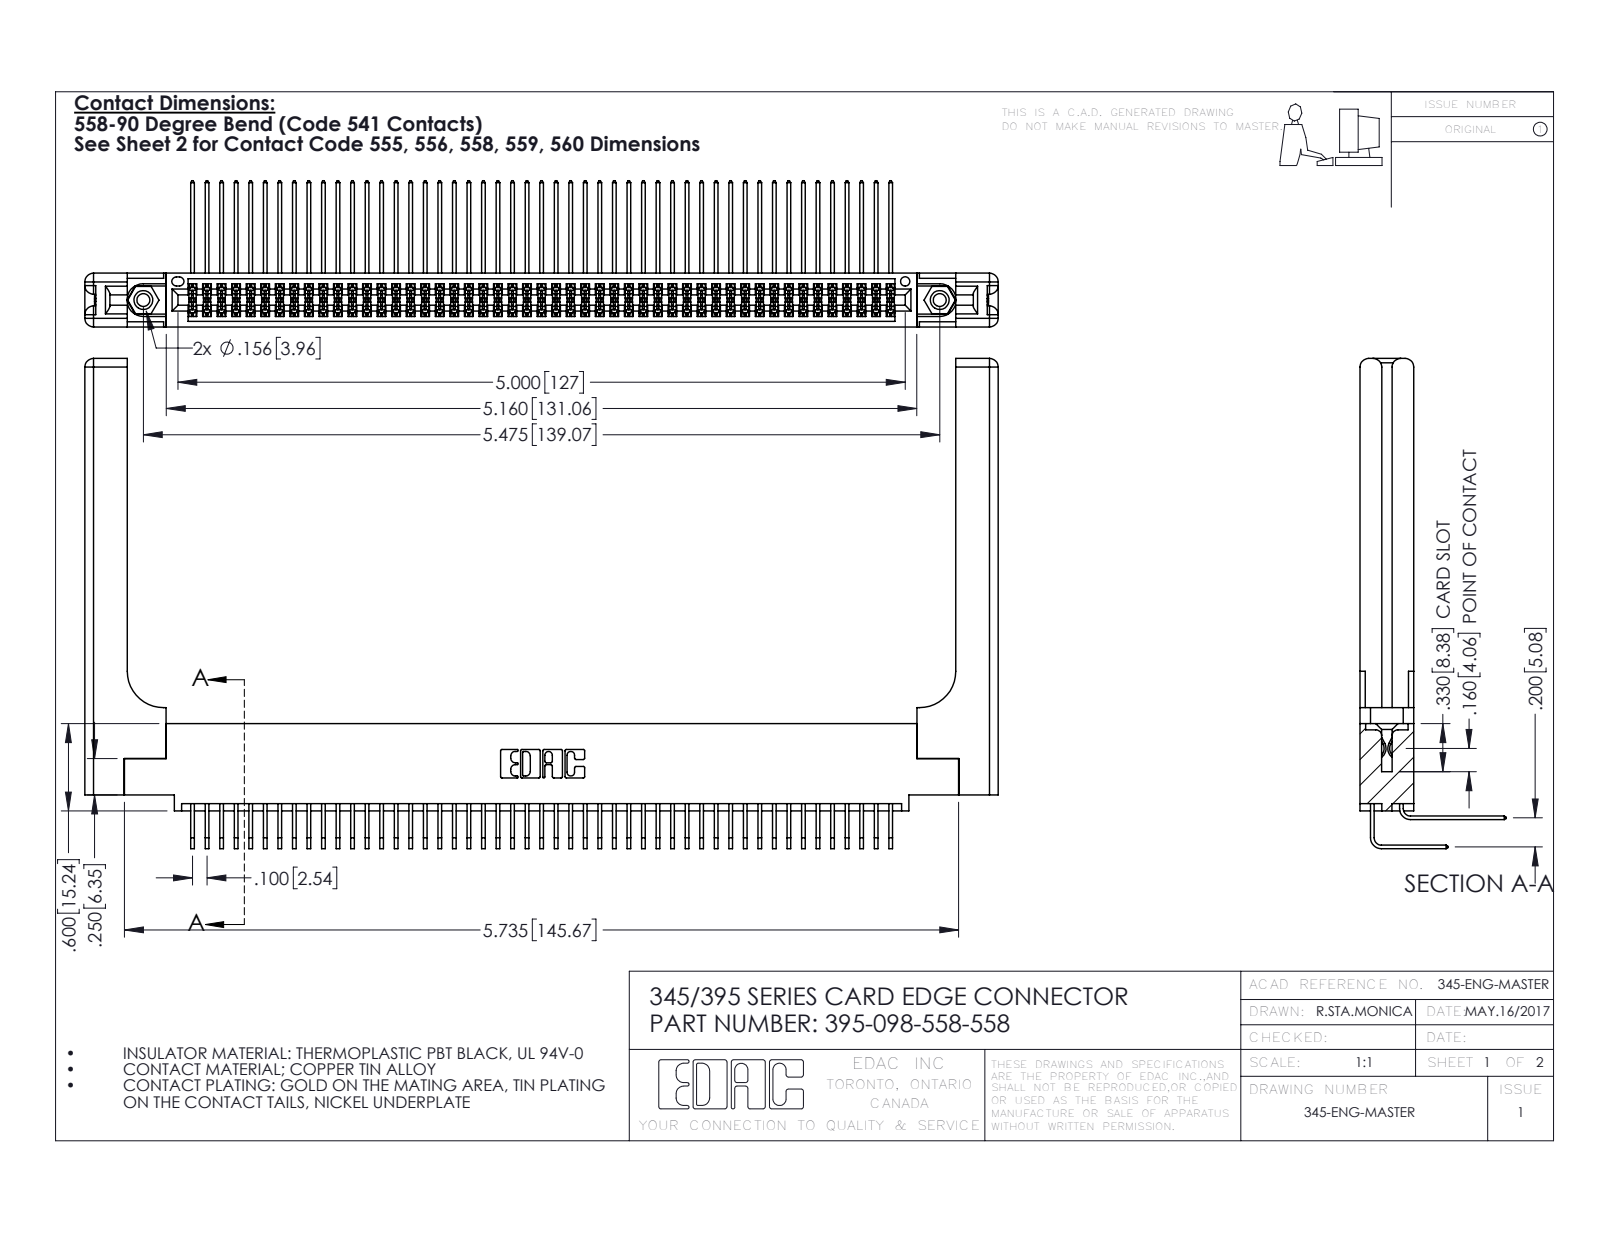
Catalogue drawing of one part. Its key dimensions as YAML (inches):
part_name: "345-292-001_558 559 Tail - 1; 345-292-001_558 Tail - 2; 345 Part_0.110 Offset - 0.156 Dia-TH; 345-250-001_345-250-001-102 (+2 more)"
step_written_by: "SolidWorks 2016 (CONFIG_CONTROL_DESIGN)"
units: inches
bodies: {solids: 103, faces: 5482, planar: 3662, cylindrical: 1760, other: 60}
overall_size: [6.279, 3.369, 1.005]
volume: 1.497
surface_area: 49.09
round_holes:
  - {diameter: 0.089, count: 2}
  - {diameter: 0.125, count: 2}
  - {diameter: 0.156, count: 2}
  - {diameter: 0.064, count: 1}
round_bosses_or_shafts:
  - {diameter: 0.155, count: 2}
partial_cylinders:
  - {radius: 0.006, count: 148}
  - {radius: 0.01, count: 22}
  - {radius: 0.06, count: 16}
  - {radius: 0.007, count: 6}
  - {radius: 0.031, count: 6}
  - {radius: 0.026, count: 3}
  - {radius: 0.014, count: 2}
  - {radius: 0.019, count: 2}
face_to_face_distances: [0.072, 0.298, 0.37, 0.2, 0.098, 0.272, 0.025, 0.225, 0.148, 0.15]
hole_center_spacings: [0.27, 5.239, 5.475]
